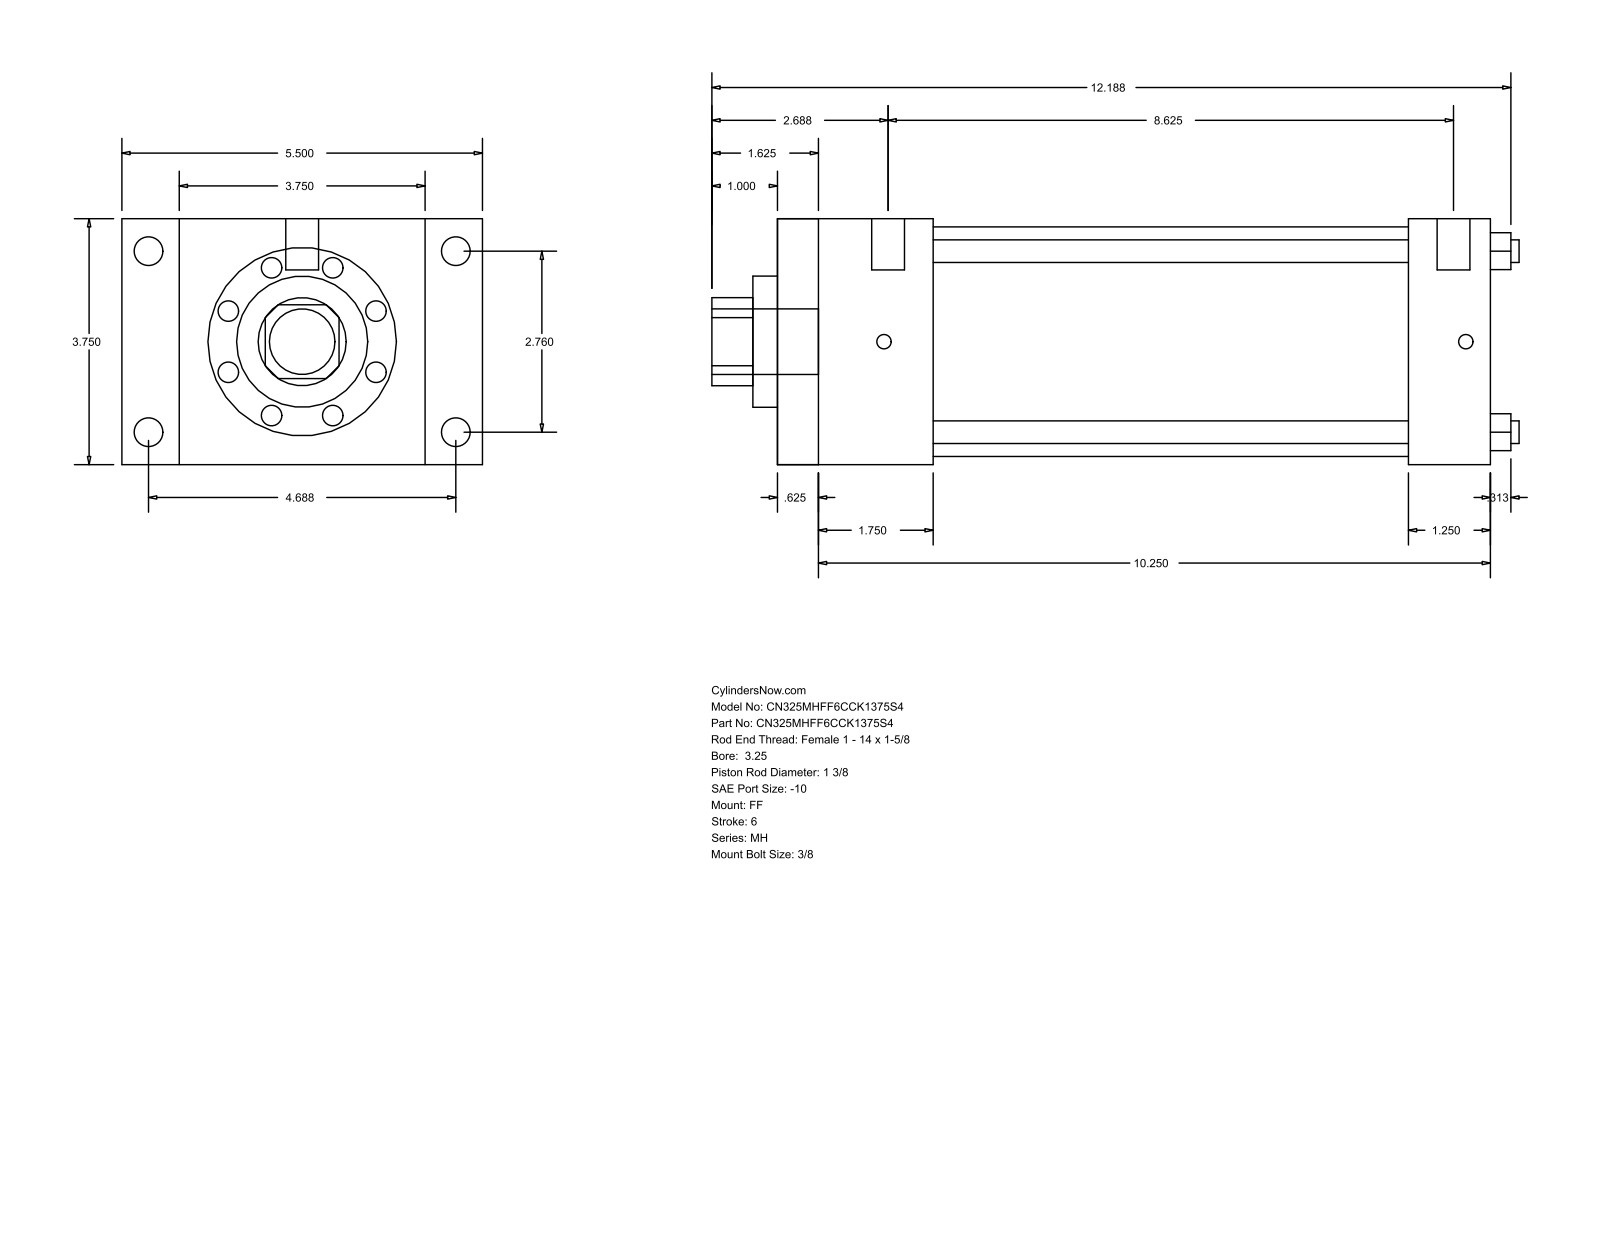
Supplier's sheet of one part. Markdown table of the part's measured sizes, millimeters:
| quantity | value |
| --- | --- |
| part name | MH_FF__0325_1.375 |
| STEP written by | GSSL Pune (CONFIG_CONTROL_DESIGN) |
| units | millimeters |
| bodies | 0 solids, 92 faces (64 planar, 28 cylindrical, 0 other) |
| overall size | 312.74 × 139.7 × 95.25 |
| round holes (diameter × count) | 8.76 × 4, 34.92 × 1, 50.8 × 1, 88.9 × 1 |
| round bosses / shafts (diameter × count) | 11.13 × 4, 5.56 × 4, 12.7 × 2, 25.4 × 1 |
| partial cylindrical surfaces (radius × count) | 17.06 × 1 |
| main face-to-face distances | 95.24, 276.22, 15.87, 260.35, 22.23, 117.47, 244.48, 228.61, 31.74, 60.32 |
| hole center spacings | 49.57, 70.1, 99.14 |
